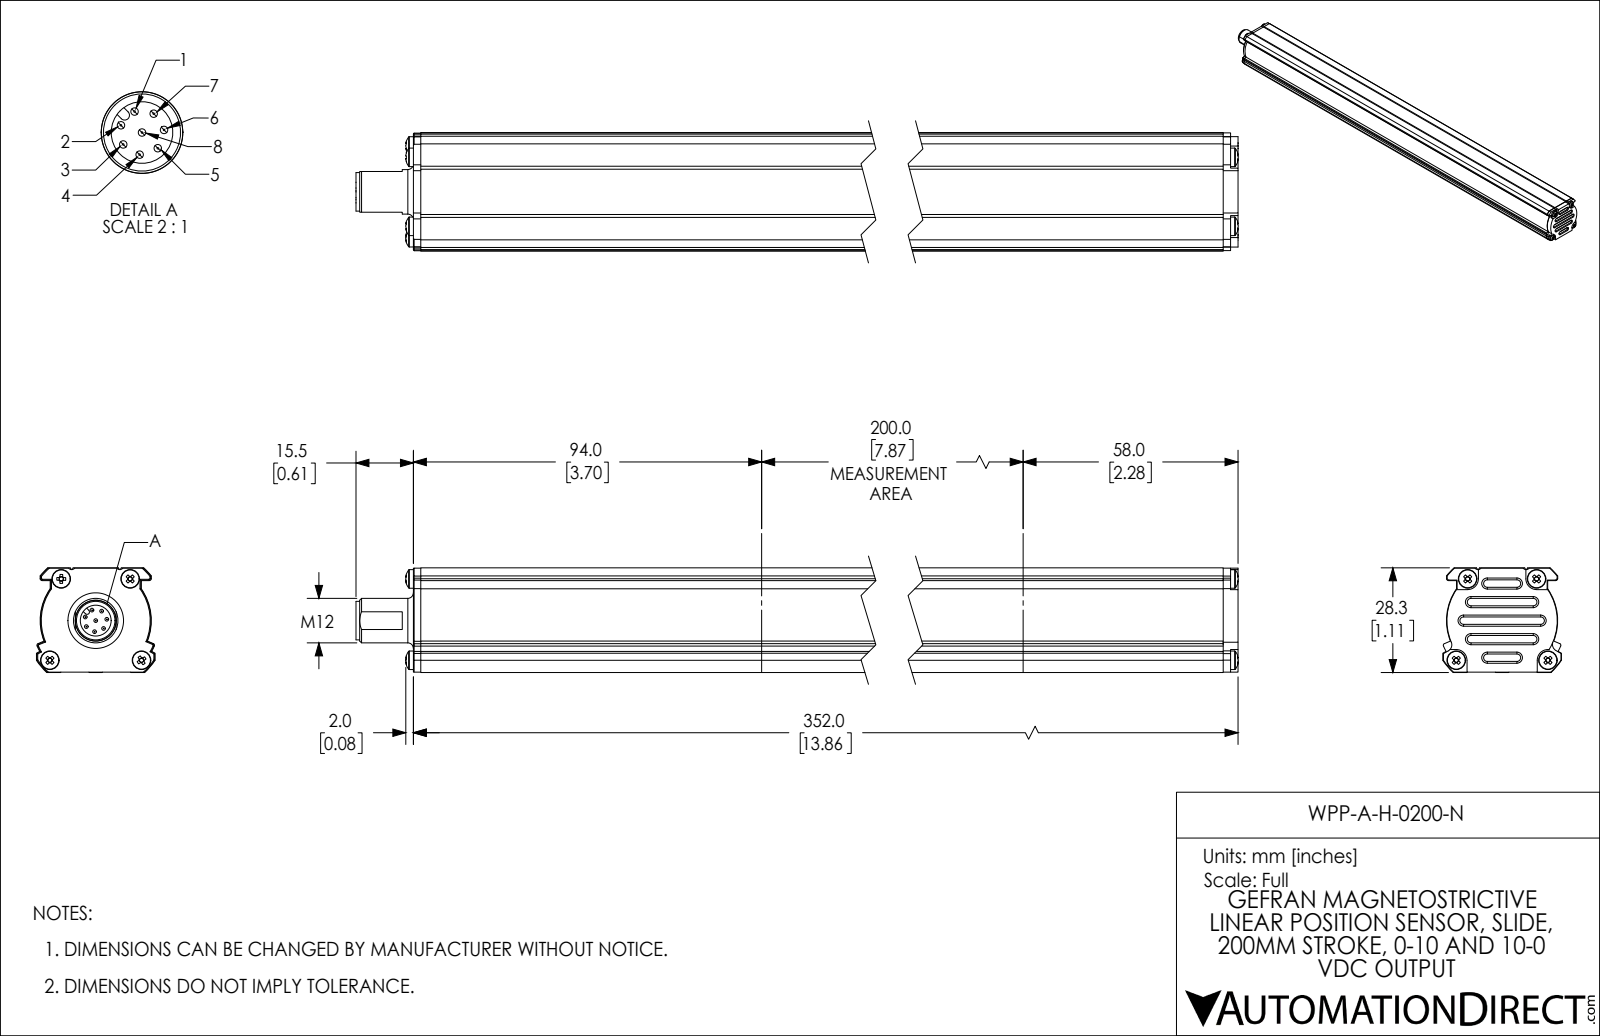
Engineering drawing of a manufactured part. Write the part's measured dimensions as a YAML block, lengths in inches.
part_name: "WPP-A-H-0200-N"
step_written_by: "SolidWorks 2021 (CONFIG_CONTROL_DESIGN)"
units: inches
bodies: {solids: 20, faces: 573, planar: 301, cylindrical: 131, other: 141}
overall_size: [14.47, 1.26, 1.112]
volume: 17.16
surface_area: 94.93
round_holes:
  - {diameter: 0.091, count: 4}
  - {diameter: 0.102, count: 4}
  - {diameter: 0.276, count: 1}
  - {diameter: 0.327, count: 1}
  - {diameter: 0.37, count: 1}
round_bosses_or_shafts:
  - {diameter: 0.039, count: 8}
  - {diameter: 0.197, count: 4}
  - {diameter: 0.472, count: 1}
  - {diameter: 0.409, count: 1}
  - {diameter: 0.376, count: 1}
  - {diameter: 0.315, count: 1}
partial_cylinders:
  - {radius: 0.02, count: 8}
  - {radius: 0.114, count: 4}
  - {radius: 0.016, count: 2}
  - {radius: 0.039, count: 2}
  - {radius: 0.073, count: 2}
  - {radius: 0.026, count: 1}
  - {radius: 0.079, count: 1}
  - {radius: 0.587, count: 1}
face_to_face_distances: [1.102, 1.112, 13.622, 0.976, 0.967, 0.136, 0.146, 1.114, 0.079, 13.701]
hole_center_spacings: [0.575, 0.644, 0.732, 0.872, 0.873, 0.974, 1.214, 1.215]
